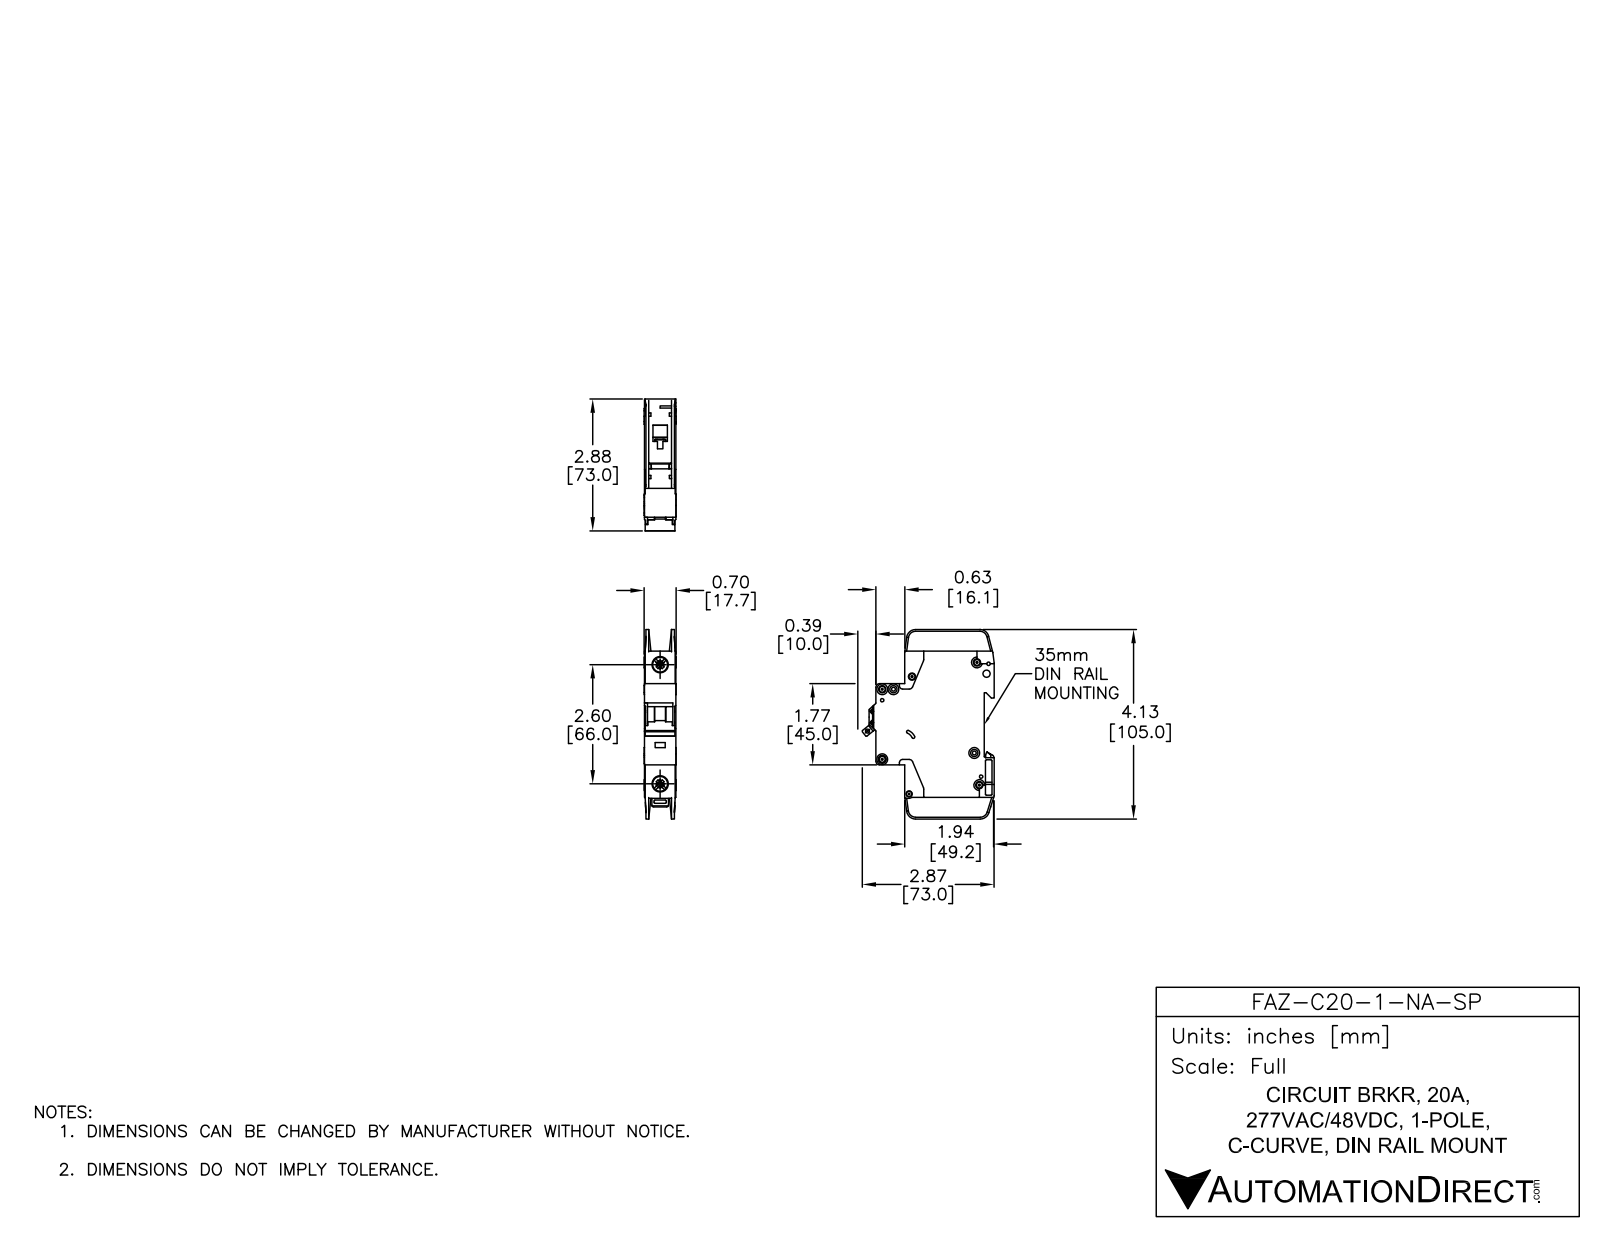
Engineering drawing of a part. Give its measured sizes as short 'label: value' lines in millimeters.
name: FAZ-C20-1-NA-SP
written by: SolidWorks 2014 (AUTOMOTIVE_DESIGN)
unit: mm
bodies: 3 solids, 784 faces (409 planar, 263 cylindrical, 112 other)
size: 105 × 73.04 × 17.7
volume: 77 695 mm³; area: 24 740 mm²
holes: 7× ⌀3.6, 2× ⌀1.09, 2× ⌀1.5, 2× ⌀4, 2× ⌀7.15, 2× ⌀8.2, 1× ⌀1.9, 1× ⌀2.15, 1× ⌀2.2, 1× ⌀2.55, 1× ⌀3.3, 1× ⌀3.4
bosses: 7× ⌀6, 1× ⌀2.5
rounds: 29× R0.25, 18× R0.5, 10× R1, 10× R2, 5× R5, 4× R4, 3× R1.8, 2× R0.2
face distances: 17.5, 15.05, 0.7, 2.45, 1.75, 15.75, 13.3, 14, 12.6, 2
hole spacings: 6.2, 5.19, 6.1, 8.19, 8.56, 8.7, 11.11, 12.45
